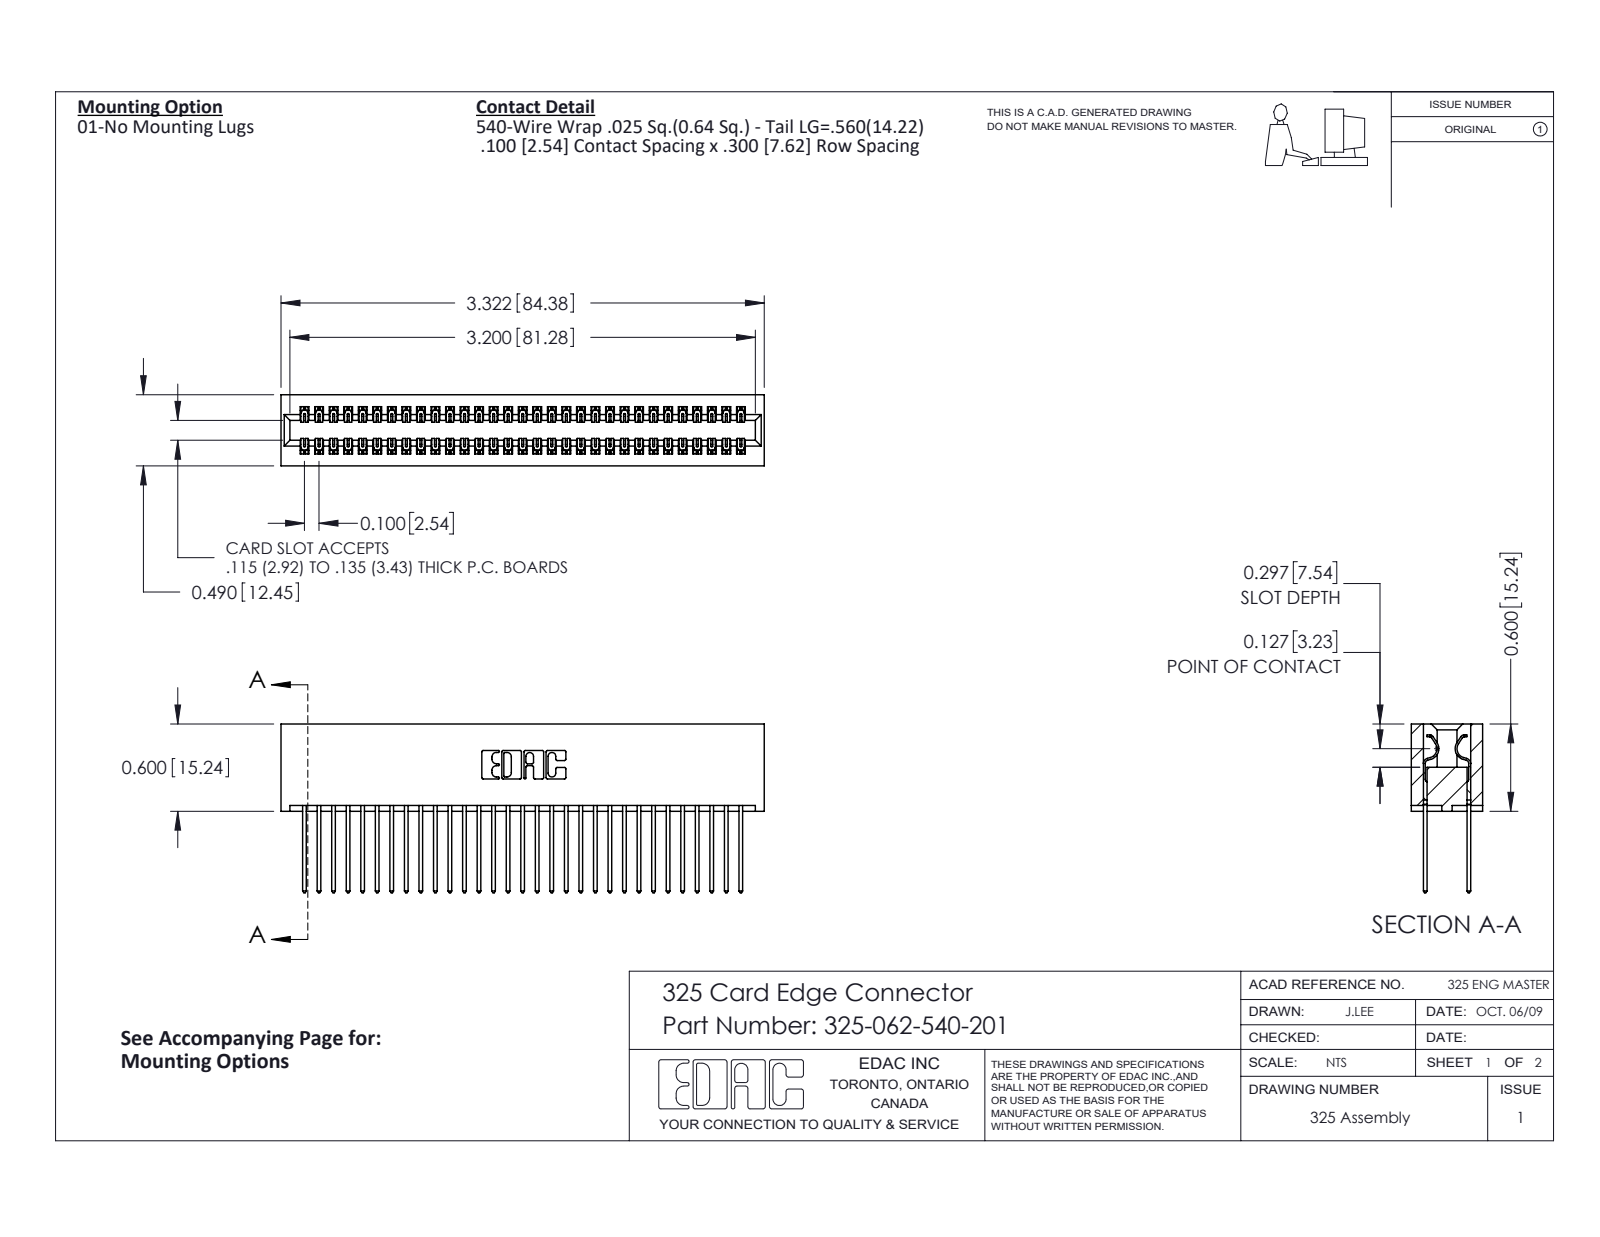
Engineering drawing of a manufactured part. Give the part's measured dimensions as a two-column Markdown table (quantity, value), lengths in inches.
| quantity | value |
| --- | --- |
| part name | 325-062-540-201; 325-292-001_325-293-140; 325 Part_Lugless |
| STEP written by | SolidWorks 2016 (CONFIG_CONTROL_DESIGN) |
| units | inches |
| bodies | 63 solids, 3330 faces (2298 planar, 1032 cylindrical, 0 other) |
| overall size | 3.322 × 1.16 × 0.49 |
| volume | 0.71 in³ |
| surface area | 24.18 in² |
| partial cylindrical surfaces (radius × count) | 0.006 × 93, 0.01 × 62, 0.01 × 22, 0.007 × 6, 0.031 × 6, 0.026 × 3, 0.014 × 2, 0.022 × 2 |
| main face-to-face distances | 0.083, 0.407, 0.3, 0.107, 0.383, 0.025, 0.325, 0.49, 0.275, 0.1 |
